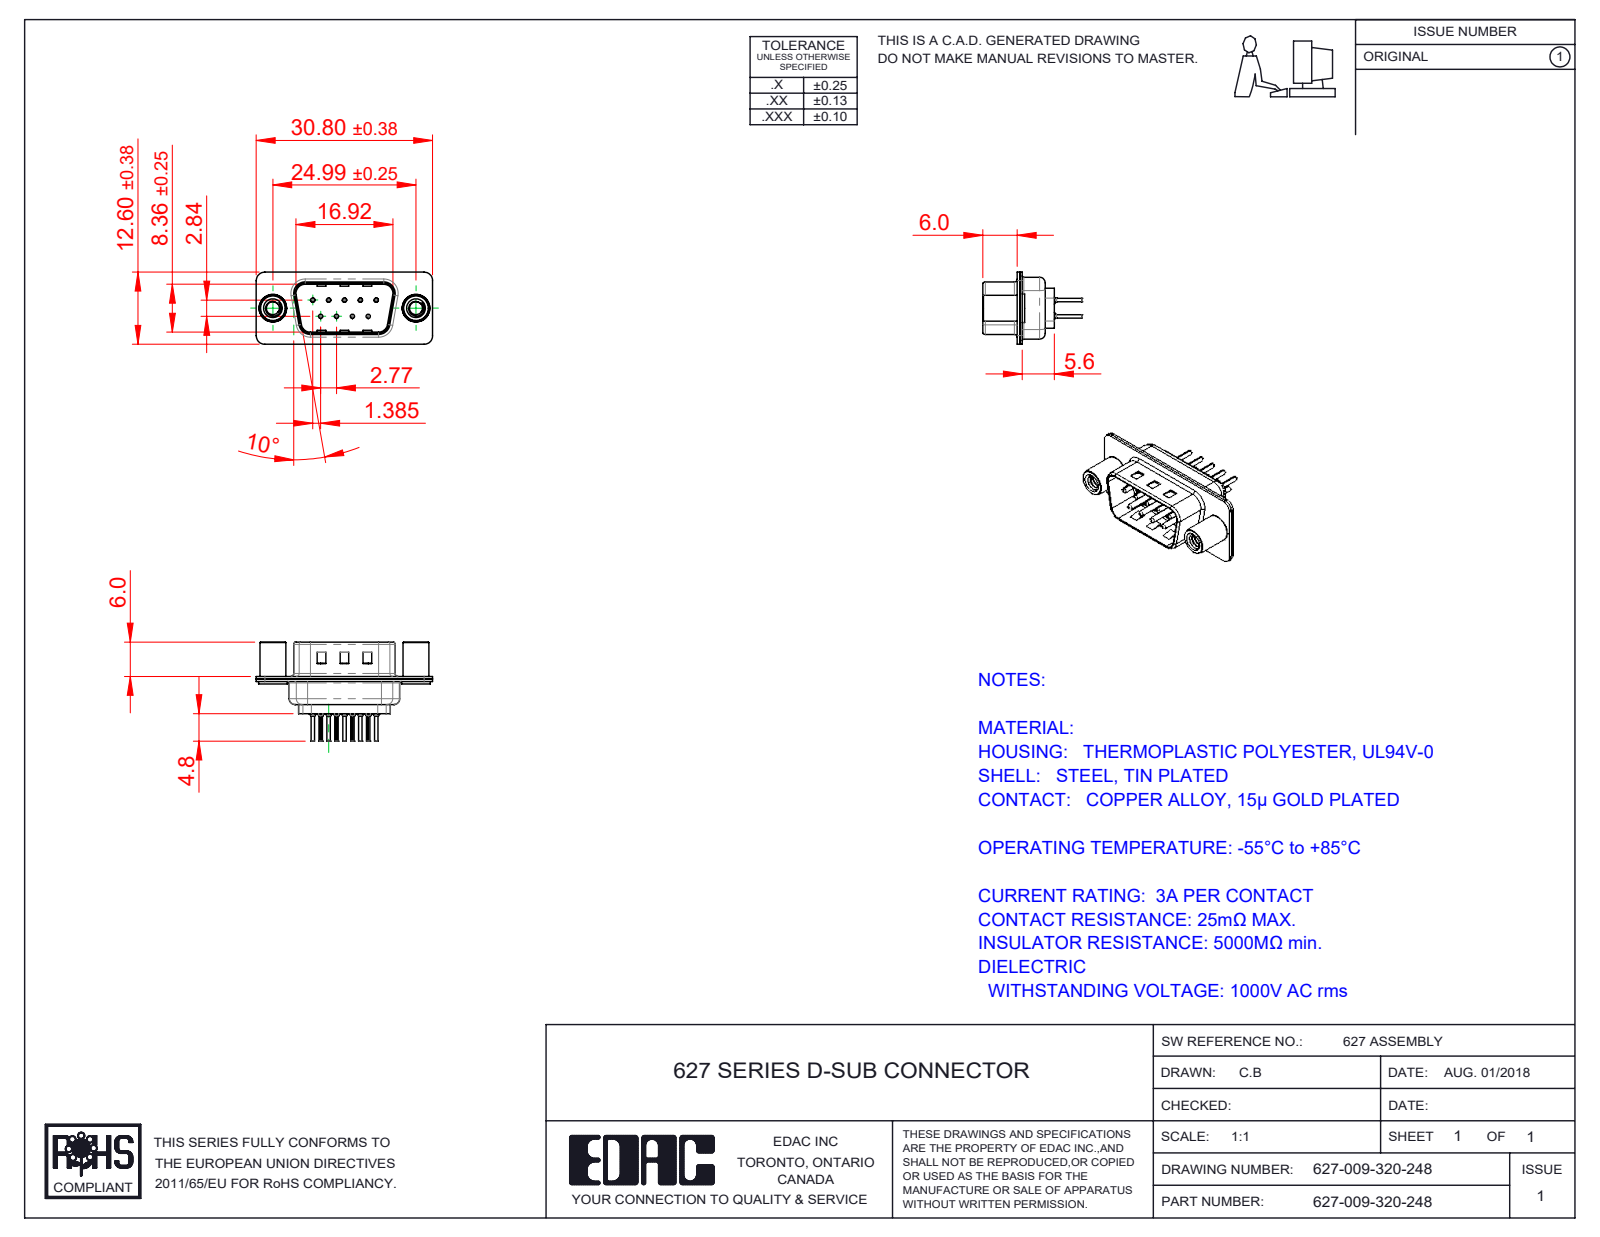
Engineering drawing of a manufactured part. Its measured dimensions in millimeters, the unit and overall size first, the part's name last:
Units: millimetres
Overall size (bounding box): 30.8 × 17.3 × 12.6
Round holes (diameter × count): ⌀0.2 ×9, ⌀0.35 ×9, ⌀1.1 ×9, ⌀1.6 ×9, ⌀2.26 ×2, ⌀4 ×2, ⌀4.8 ×2
Round bosses / shafts (diameter × count): ⌀2 ×9, ⌀1.5 ×9, ⌀0.75 ×9, ⌀0.6 ×9, ⌀5 ×2, ⌀4.9 ×2, ⌀4.5 ×2
Partial cylindrical surfaces — rounded edges, fillets, slot ends (radius × count): R0.1 ×18, R1.5 ×18, R2 ×12, R0.5 ×8, R1.6 ×8, R0.25 ×4, R0.6 ×4, R0.65 ×4
Main face-to-face distances: 0.4, 0.45, 0.9, 0.82, 9.58, 1.4, 8.76, 0.5, 1.5, 5.6
Hole centre spacings: 3.16, 2.77, 5.54, 5.03, 5.04, 8.31, 7.48, 7.49
Volume: 1 375 mm³ · Surface area: 4 129 mm²
Bodies: 14 solids, 1220 faces (325 planar, 490 cylindrical, 405 other)
Part name (STEP PRODUCT): 627 4-40 Threaded Standoff; 627 Contact Row 2_20L; 627 Housing_09 LP; 627-009-320-248 (+3 more)
STEP written by: SolidWorks 2020 (CONFIG_CONTROL_DESIGN)
